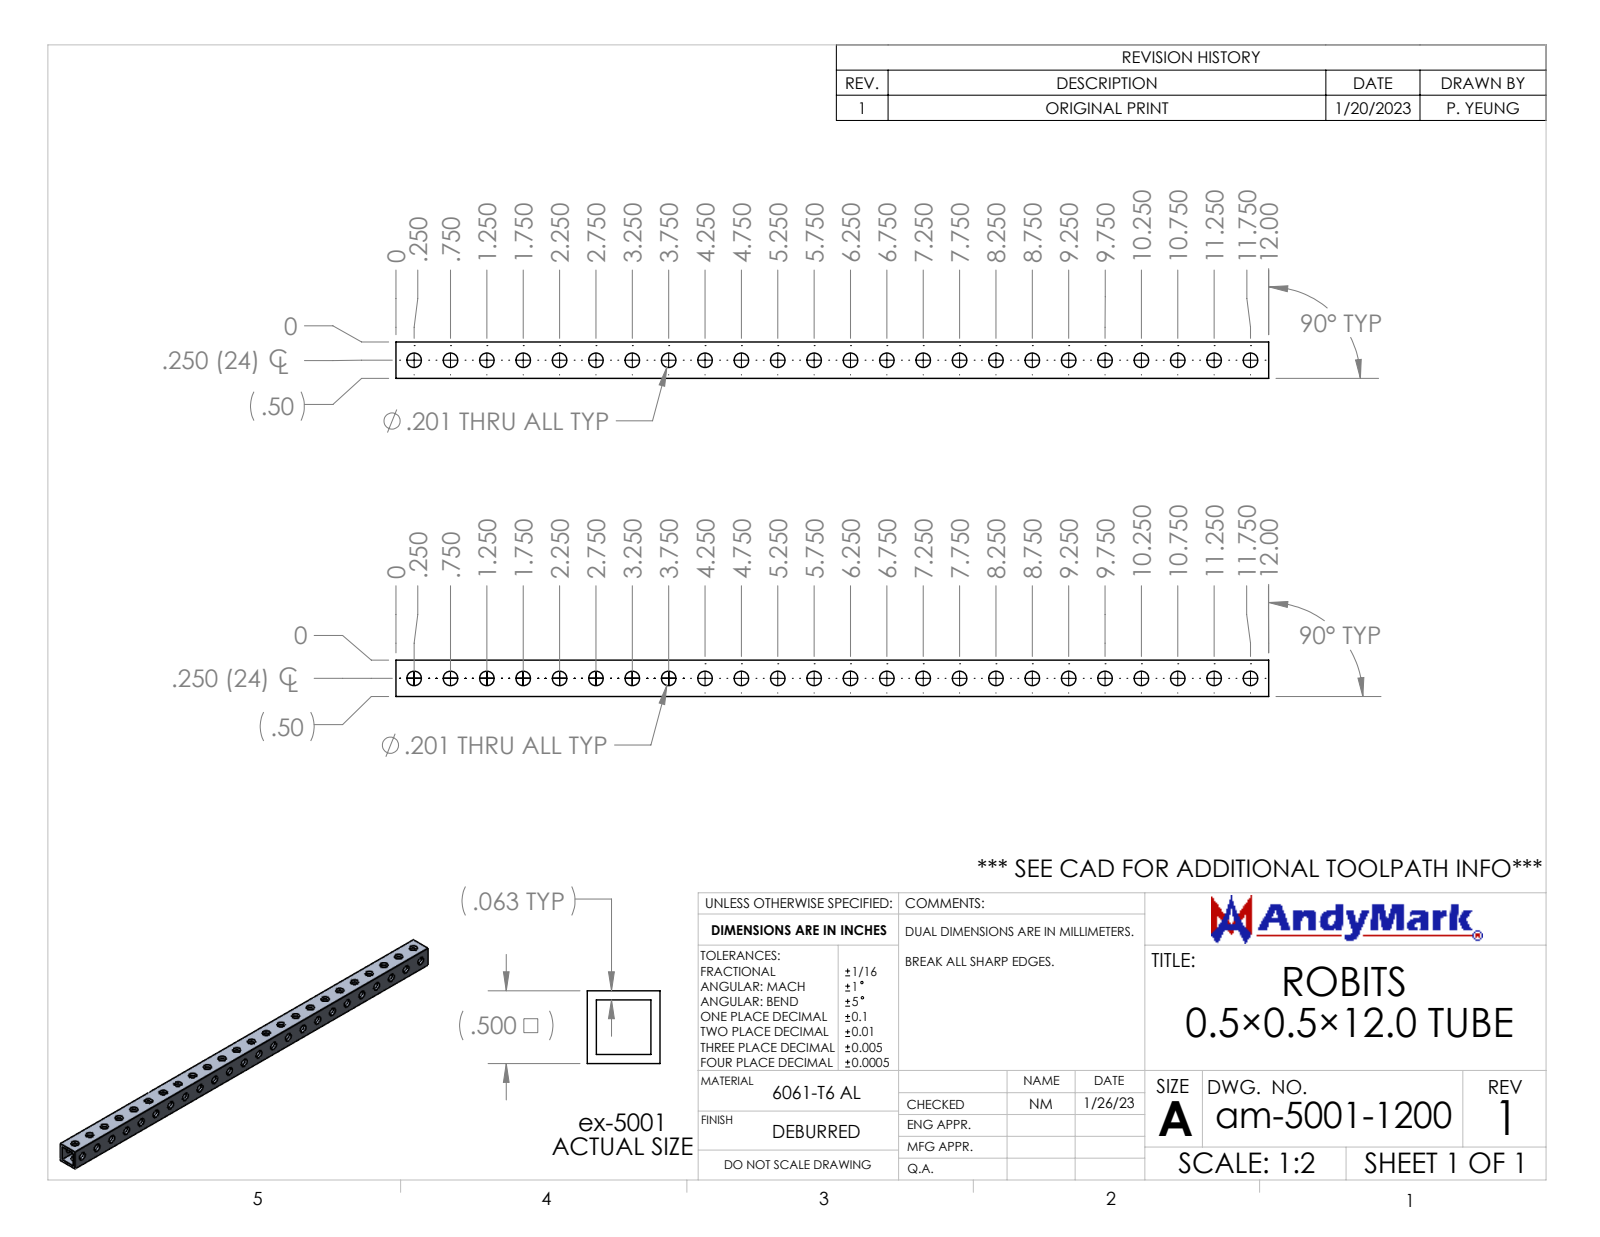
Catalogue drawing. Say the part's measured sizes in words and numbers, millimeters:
The part is named "am-5001-1200 RoBits 0.5×0.5×12.0 Tube". Its 3-D file was written by "SolidWorks 2022 (CONFIG_CONTROL_DESIGN)". It is 1 solid with 202 faces: 10 planar, 192 cylindrical and 0 other. Overall it measures 304.8 by 12.7 by 12.7 millimeters. Its volume is 18 390 cubic millimeters and its surface area 25 750 square millimeters. Round holes: 48 of diameter 5.1. The main face-to-face distances are 1.6, 11.1, 12.7, 9.5, 304.8. The hole center spacings are 12.7, 25.4, 38.1, 50.8, 63.5, 76.2, 88.9, 101.6.
